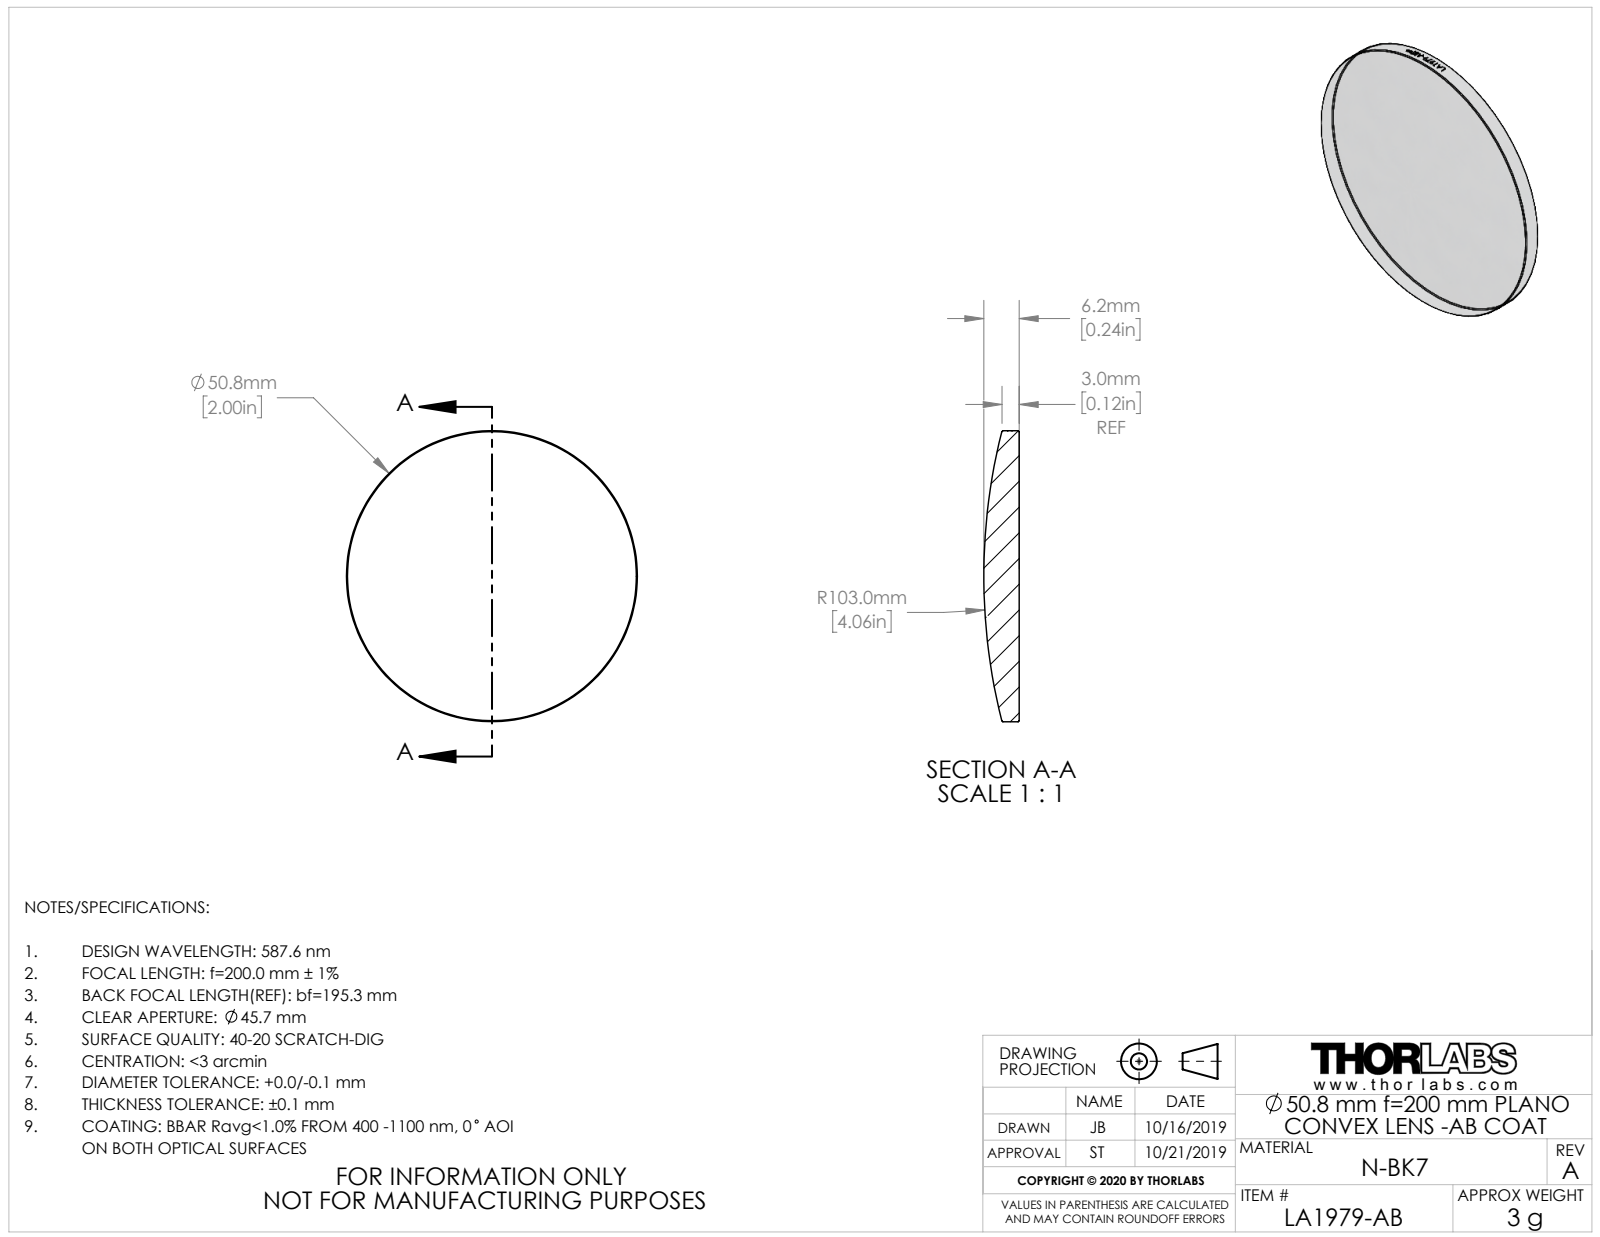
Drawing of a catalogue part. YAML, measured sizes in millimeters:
part_name: "TTN195801-E0W"
step_written_by: "SolidWorks 2018 (CONFIG_CONTROL_DESIGN)"
units: millimeters
bodies: {solids: 1, faces: 28, planar: 1, cylindrical: 21, other: 6}
overall_size: [50.8, 50.8, 6.18]
volume: 9315
surface_area: 4537
round_bosses_or_shafts:
  - {diameter: 50.8, count: 1}
